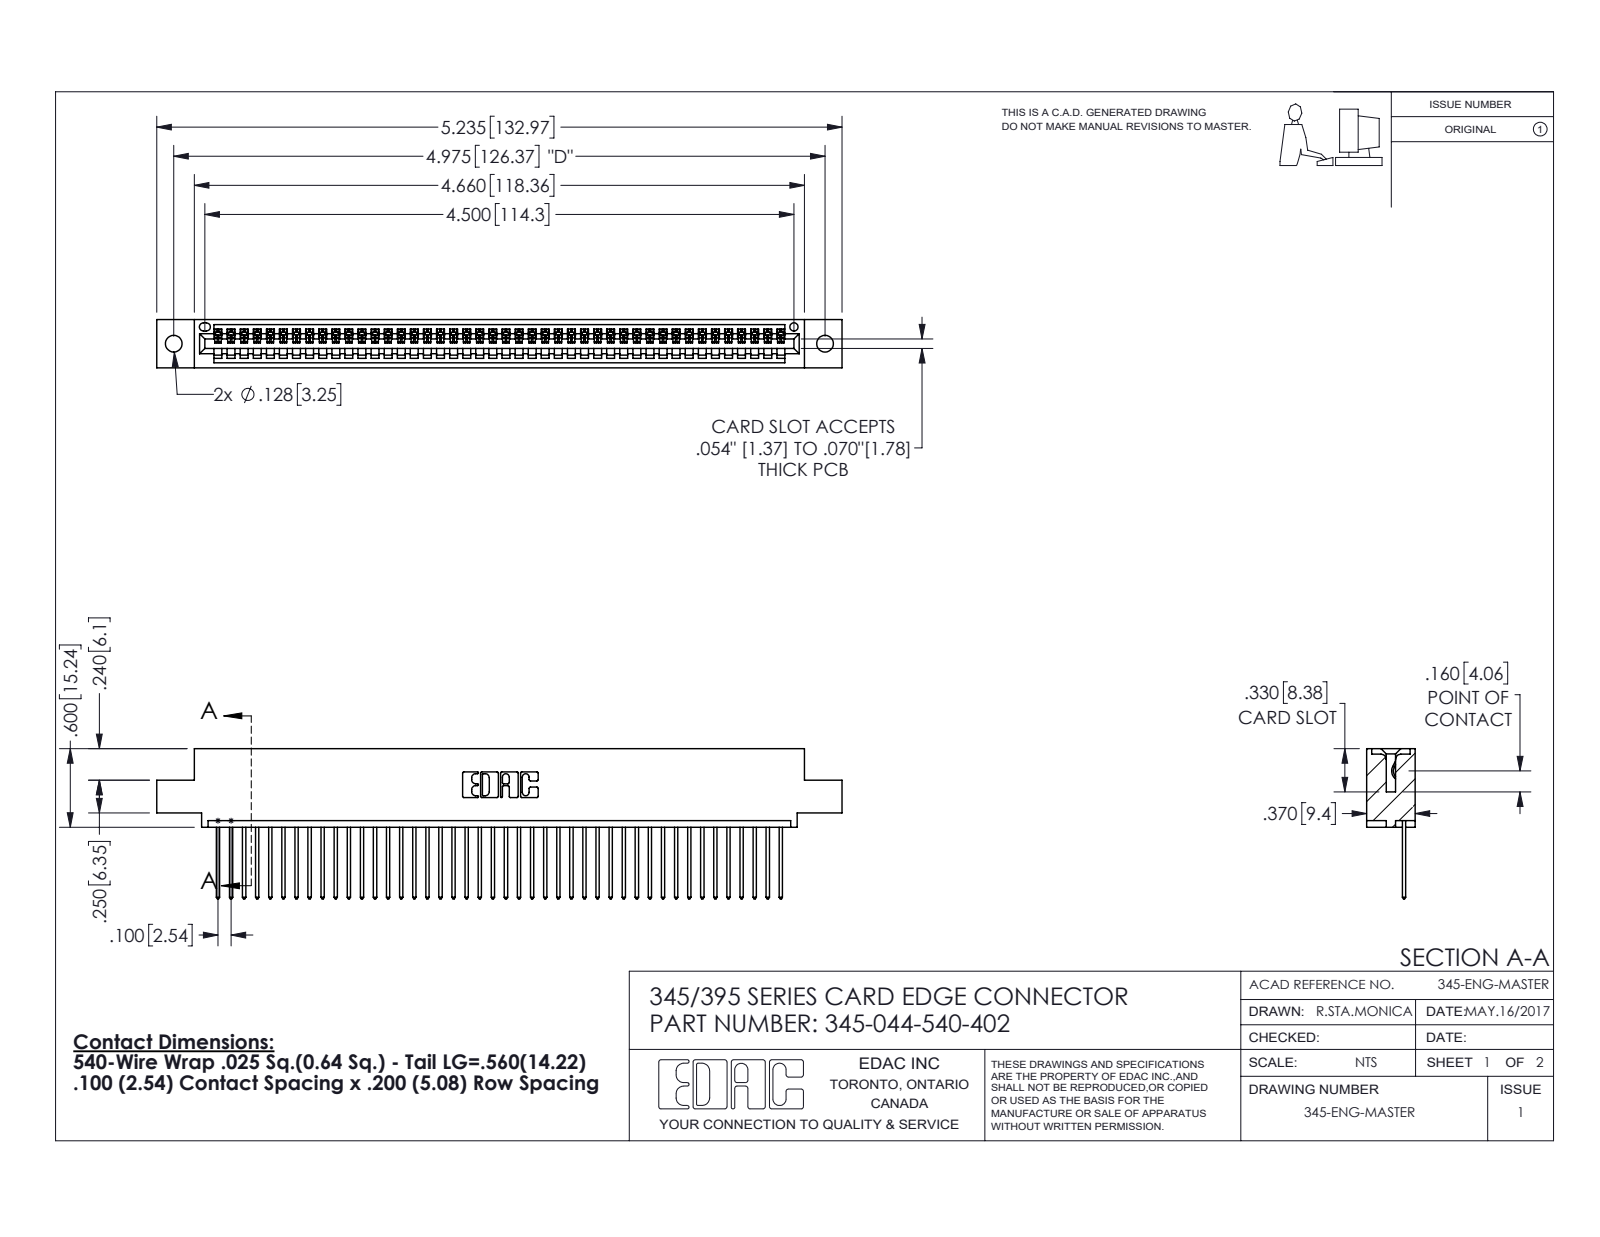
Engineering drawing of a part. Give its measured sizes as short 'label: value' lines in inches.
name: 345-044-540-402; 345-292-001_345-293-140; 345 Part_0.110 Offset - 0.128 Dia
written by: SolidWorks 2016 (CONFIG_CONTROL_DESIGN)
unit: in
bodies: 45 solids, 2682 faces (1844 planar, 838 cylindrical, 0 other)
size: 5.235 × 1.147 × 0.37
volume: 0.769 in³; area: 26.36 in²
holes: 2× ⌀0.128, 1× ⌀0.064
rounds: 88× R0.006, 88× R0.01, 22× R0.01, 6× R0.007, 6× R0.031, 3× R0.026, 2× R0.031, 2× R0.04
face distances: 0.298, 0.072, 0.37, 0.098, 0.272, 0.025, 0.2, 0.225, 0.149, 0.072
hole spacings: 0.27, 4.739, 4.975
